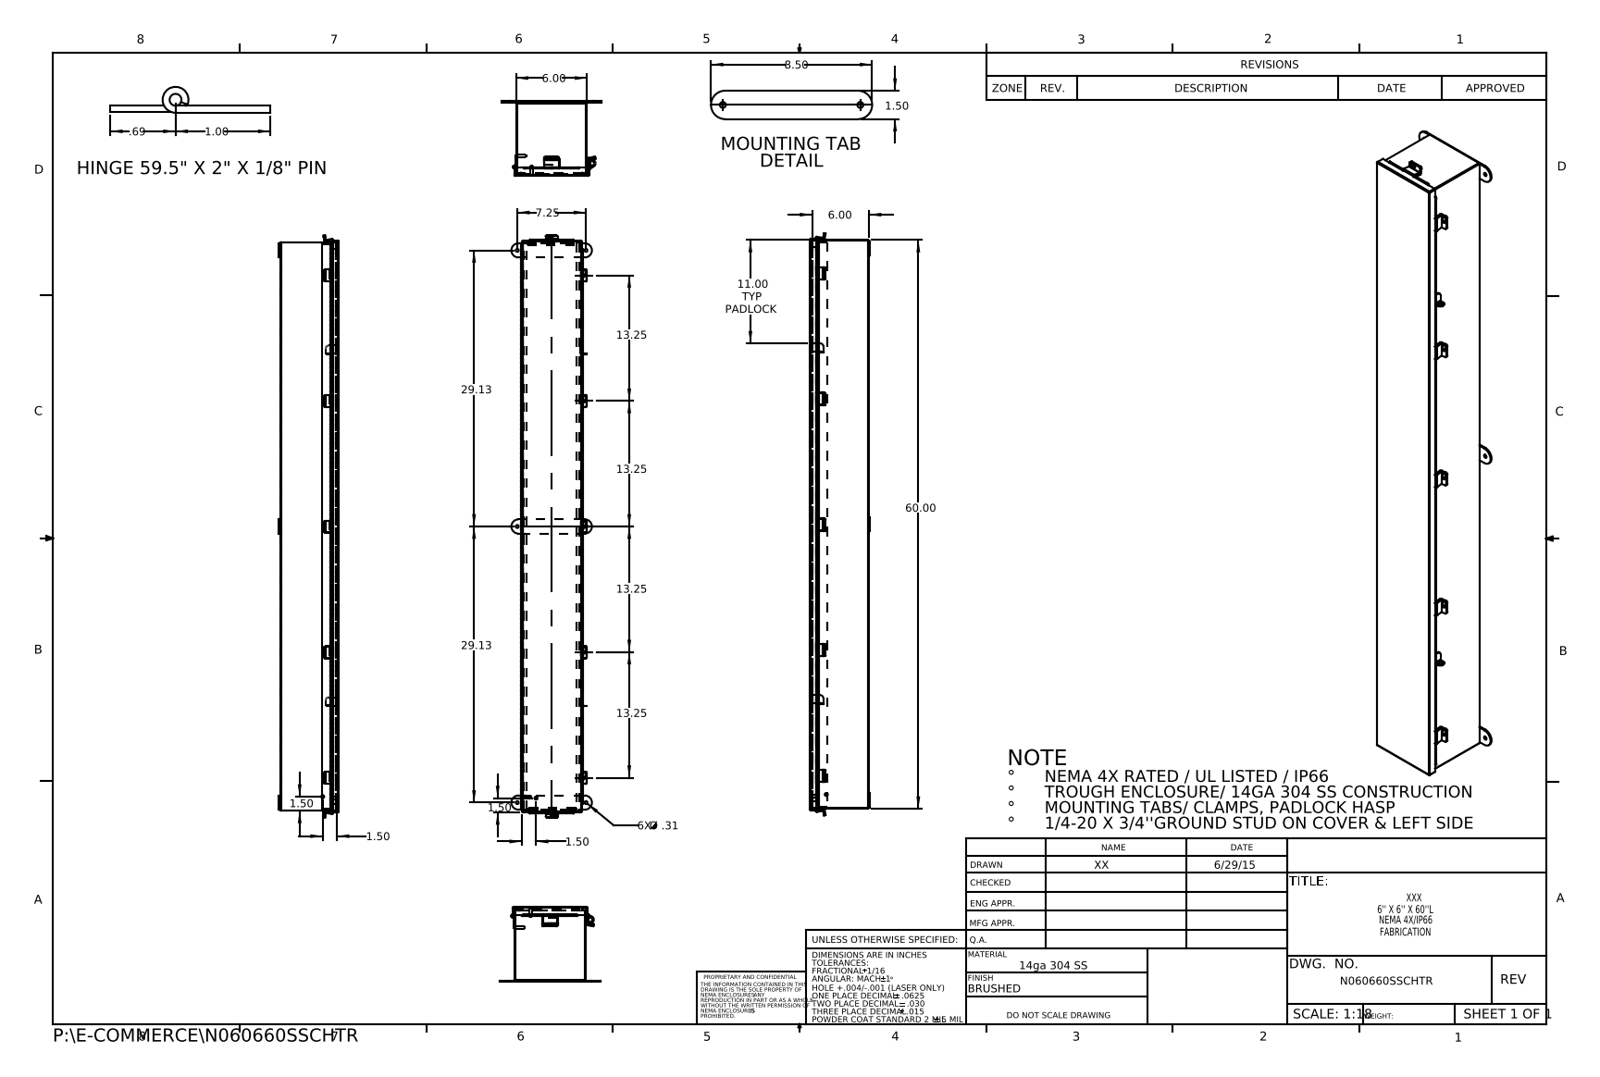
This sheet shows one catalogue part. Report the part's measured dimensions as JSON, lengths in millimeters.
{"part_name": "N060660SSCHTR JIC Top; N060660SSCHTR JIC Cover Clamp; N060660SSCHTR JIC Clamp Bracket; N060660SSCHTR JIC_Cover_Template (+8 more)", "step_written_by": "SolidWorks 2015 (CONFIG_CONTROL_DESIGN)", "units": "millimeters", "bodies": {"solids": 27, "faces": 1657, "planar": 986, "cylindrical": 651, "other": 20}, "overall_size": [1559.7, 215.9, 161], "volume_mm3": 2260000, "surface_area_mm2": 2395000, "round_holes": [[6.4, 7], [8, 6], [3.2, 1], [9.5, 1]], "round_bosses_or_shafts": [[8, 2], [6, 2], [6.9, 1], [6.4, 1]], "partial_cylinders_radius": [[3.2, 27], [3.4, 14], [0.2, 12], [0.3, 12], [2.2, 12], [2.1, 6], [2.5, 6], [19.1, 6]], "face_to_face_distances": [1.9, 150.5, 155.7, 152.4, 148.6, 157.6, 153.7, 3.8, 154.3, 1.9], "hole_center_spacings": [336.6, 739.8, 184.2, 673.1, 762.4, 762.4, 1009.7, 1479.6]}
